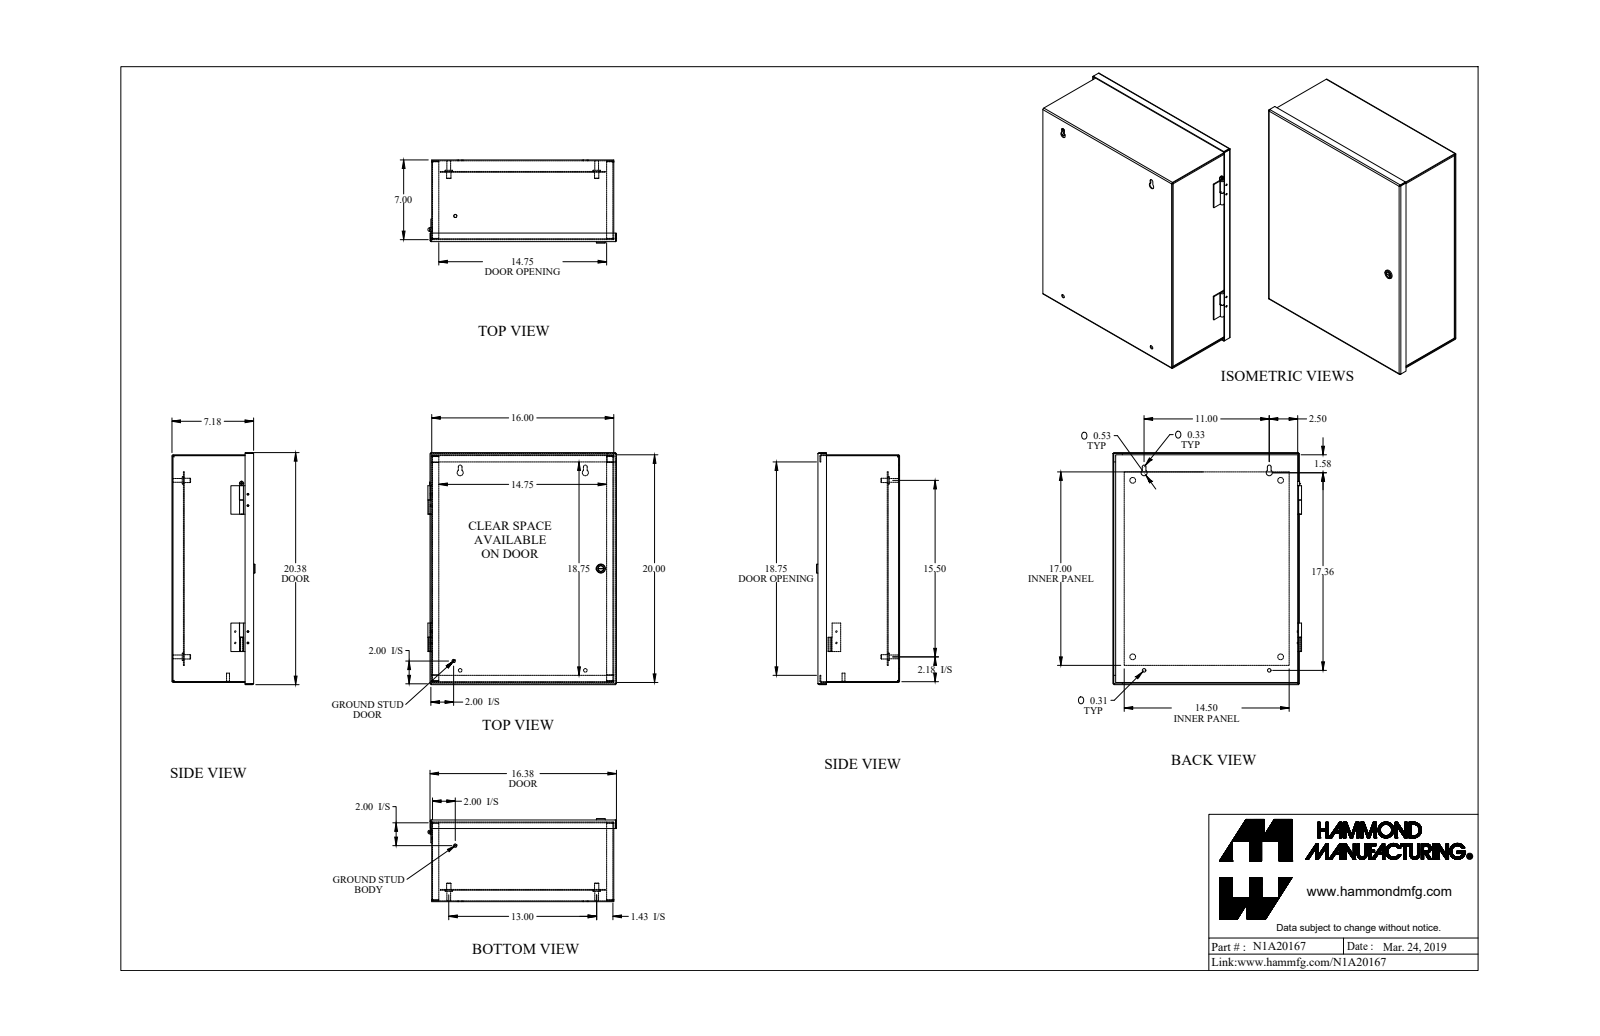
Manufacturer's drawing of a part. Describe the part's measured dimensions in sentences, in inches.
The part is named "N1A20167". Its 3-D file was written by "SolidWorks 2018 (AUTOMOTIVE_DESIGN)". It is 23 solids with 520 faces: 294 planar, 182 cylindrical and 44 other. Overall it measures 20.384 by 16.574 by 7.299 inches. Its volume is 111.4 cubic inches and its surface area 3 102 square inches. Round holes: 8 of diameter 0.14, 4 of diameter 0.5, 2 of diameter 0.307, 2 of diameter 0.312, 2 of diameter 0.445, 1 of diameter 0.17, 1 of diameter 0.187, 1 of diameter 0.516. Round bosses or shafts: 8 of diameter 0.128, 5 of diameter 0.375, 4 of diameter 0.65, 4 of diameter 0.33, 2 of diameter 1, 2 of diameter 0.281, 2 of diameter 0.25, 1 of diameter 0.788. Partial cylindrical surfaces (rounded edges, fillets, slot ends): 16 of radius 0.036, 16 of radius 0.108, 2 of radius 0.06, 2 of radius 0.153, 2 of radius 0.164, 2 of radius 0.266, 1 of radius 0.03, 1 of radius 0.125. The main face-to-face distances are 0.072, 7.105, 1.009, 6.096, 7.033, 7.177, 15.928, 1.081, 6.024, 0.937. The hole center spacings are 1, 1.119, 1.104, 1.553, 2.031, 7.758, 12.059, 12.062.
